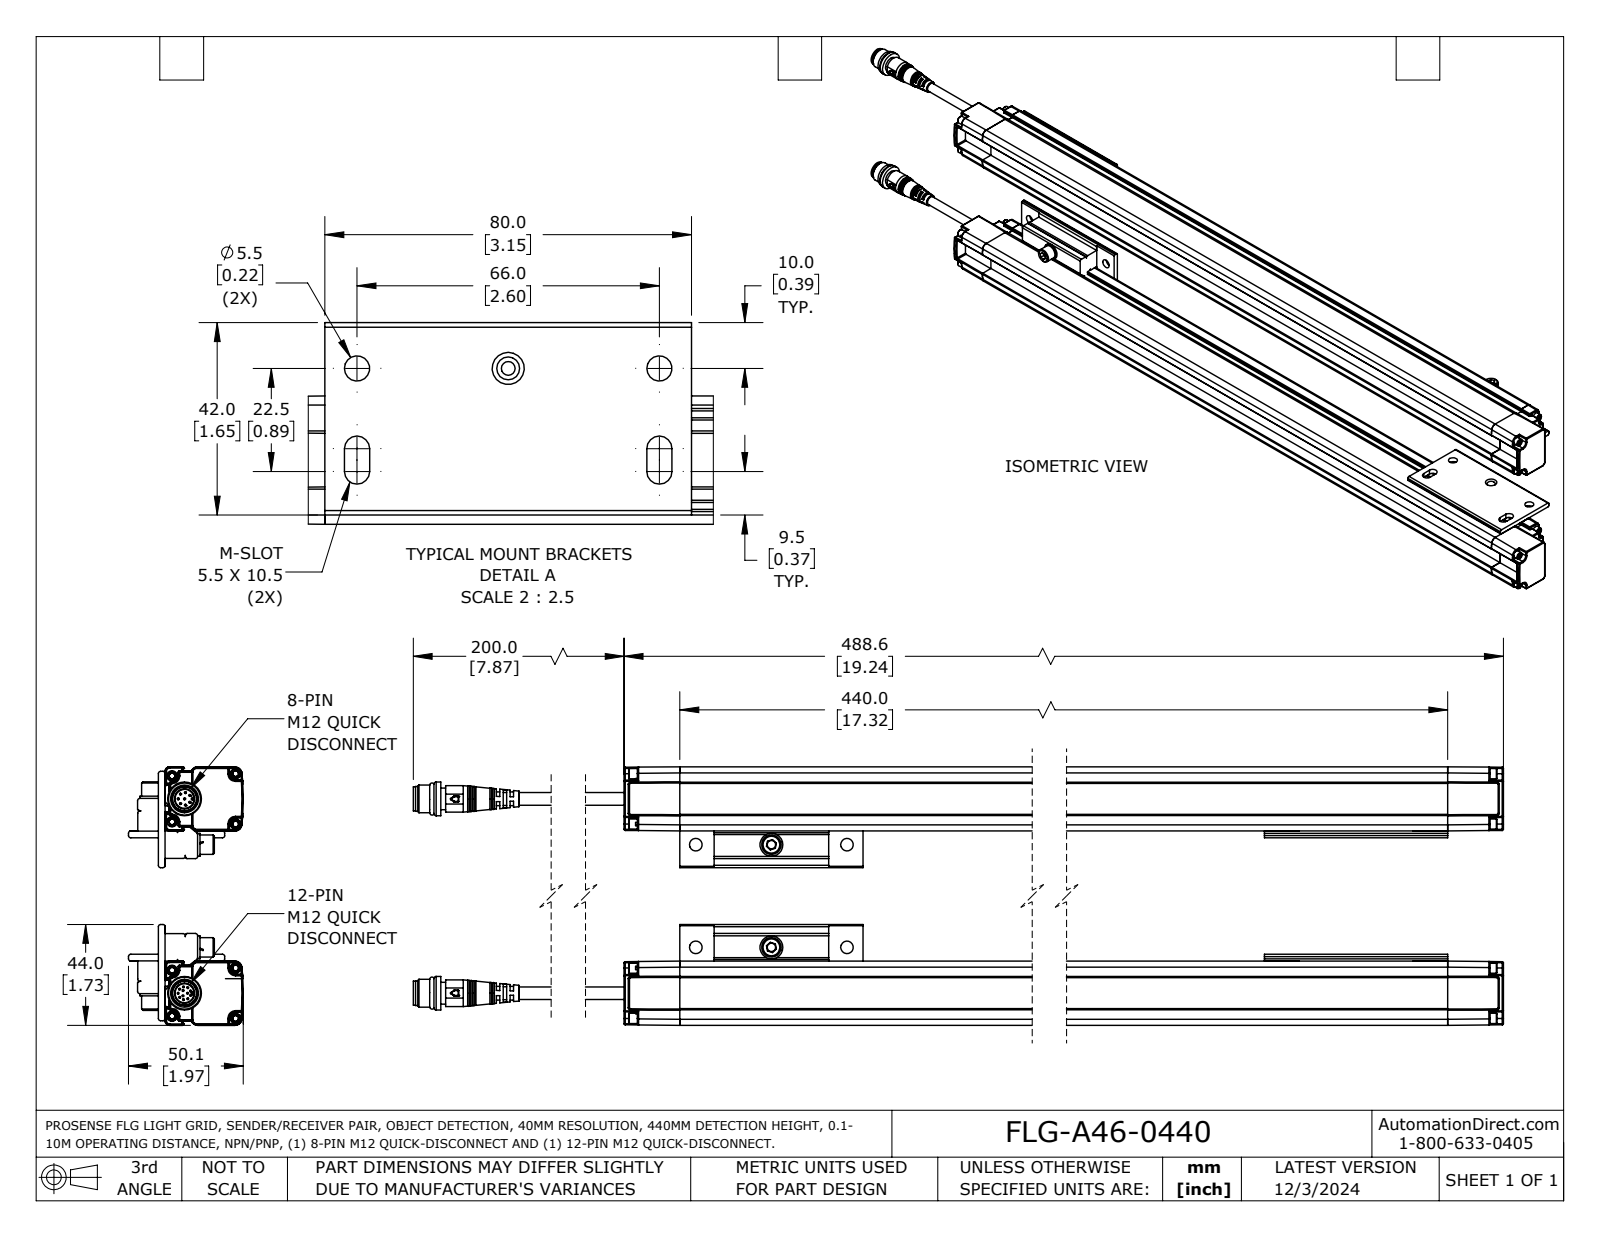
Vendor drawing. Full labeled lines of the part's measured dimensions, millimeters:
Part name (STEP PRODUCT): FLG-A46-0440
STEP written by: SolidWorks 2023 (AUTOMOTIVE_DESIGN)
Units: millimetres
Bodies: 10 solids, 1668 faces (816 planar, 456 cylindrical, 396 other)
Overall size (bounding box): 580.55 × 112.8 × 50.09
Volume: 830 540 mm³ · Surface area: 229 396 mm²
Round holes (diameter × count): ⌀0.4 ×16, ⌀5.5 ×6, ⌀2.5 ×4, ⌀5 ×3, ⌀8.3 ×2
Round bosses / shafts (diameter × count): ⌀0.8 ×20, ⌀4.5 ×8, ⌀3 ×8, ⌀5.5 ×4, ⌀1.5 ×4, ⌀10 ×3, ⌀8.5 ×3, ⌀3.7 ×3
Partial cylindrical surfaces — rounded edges, fillets, slot ends (radius × count): R0.5 ×142, R1 ×40, R0.25 ×20, R0.2 ×12, R0.3 ×12, R2.75 ×12, R2.55 ×6, R1.25 ×4
Main face-to-face distances: 84.8, 28, 1.8, 7.25, 20.75, 3, 56.8, 24.65, 26.45, 112.8
Hole centre spacings: 2.75, 33, 4.15, 24.87, 55.64, 5.45, 44.8, 66
